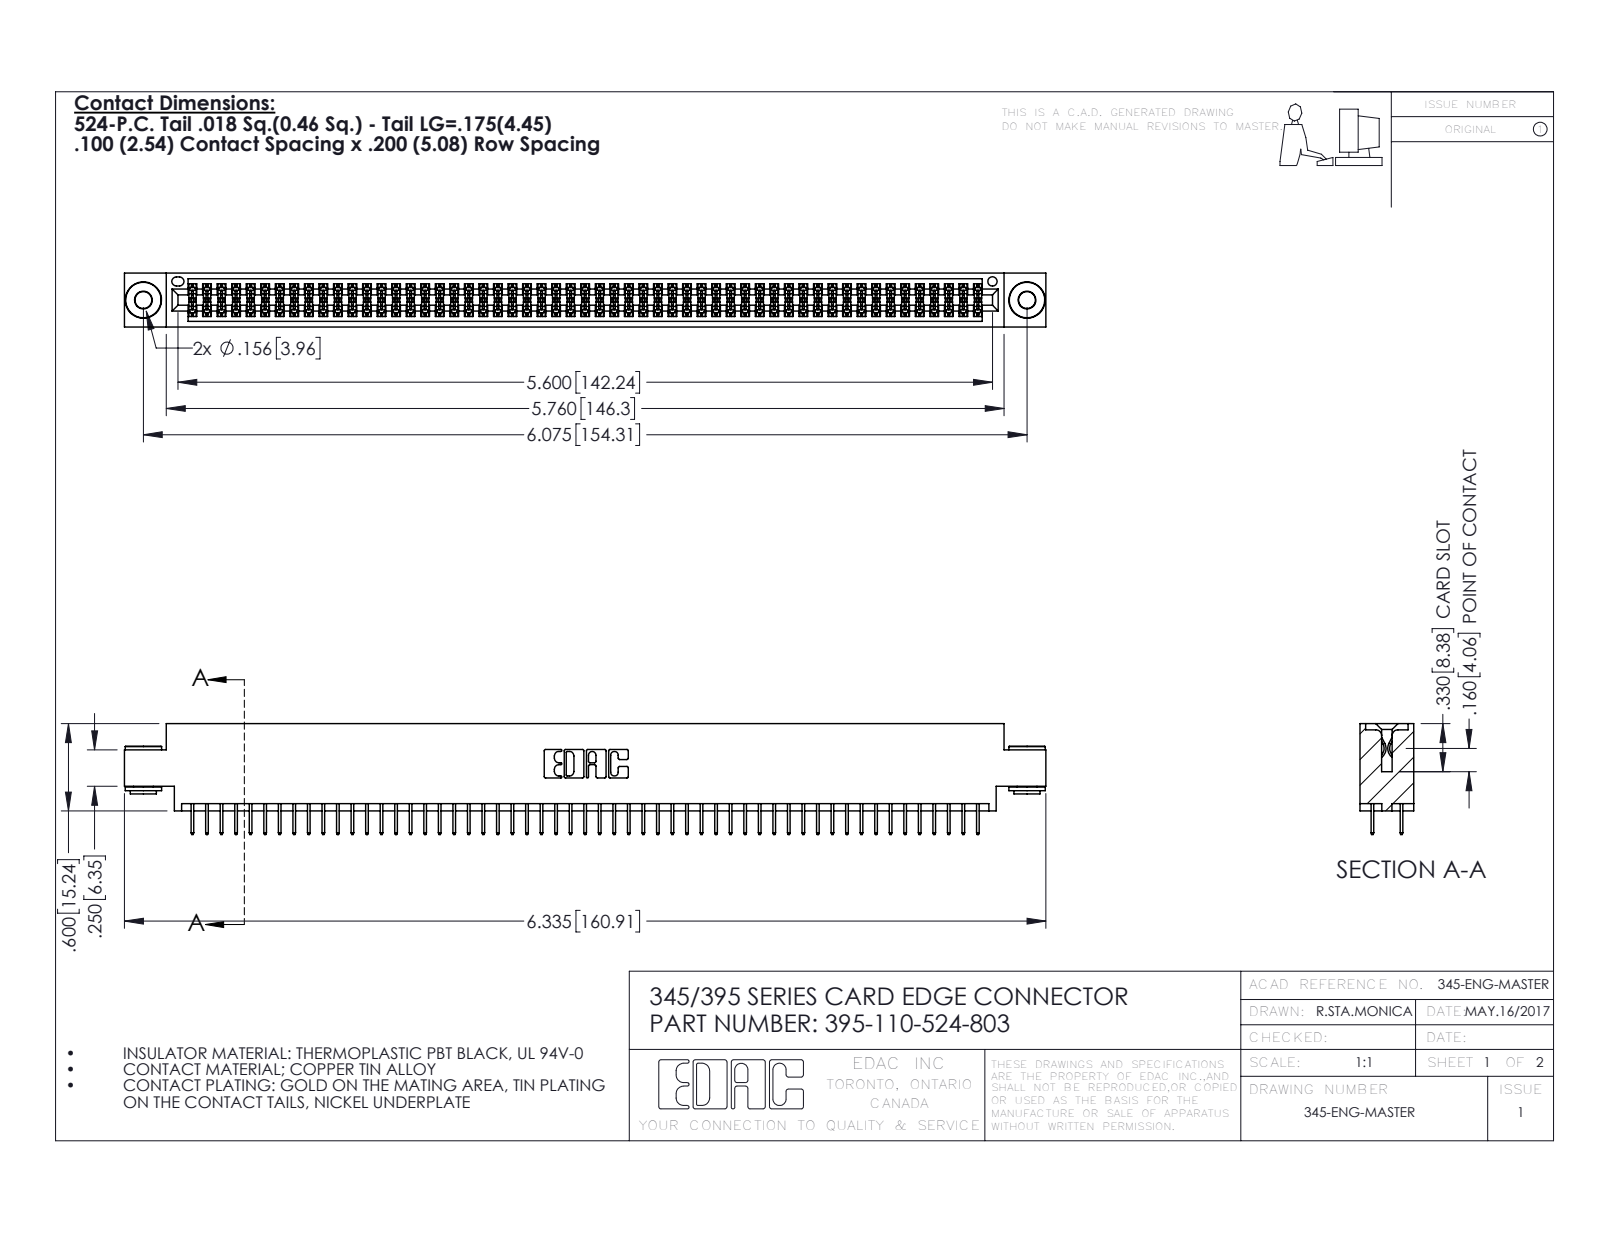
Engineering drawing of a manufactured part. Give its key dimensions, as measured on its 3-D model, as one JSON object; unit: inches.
{"part_name": "345-292-001_345-293-124; 345-250-002_345-250-002-102; 345 Part_0.170 Offset - 0.156 Dia-TH; 395-110-524-803", "step_written_by": "SolidWorks 2016 (CONFIG_CONTROL_DESIGN)", "units": "inches", "bodies": {"solids": 113, "faces": 6108, "planar": 4384, "cylindrical": 1716, "other": 8}, "overall_size": [6.335, 0.762, 0.37], "volume_in3": 0.945, "surface_area_in2": 35.74, "round_holes": [[0.116, 2], [0.156, 2], [0.064, 1]], "round_bosses_or_shafts": [[0.25, 2], [0.18, 2], [0.136, 2]], "partial_cylinders_radius": [[0.006, 165], [0.01, 22], [0.007, 6], [0.031, 6], [0.026, 3], [0.014, 2], [0.019, 2], [0.022, 2]], "face_to_face_distances": [0.072, 0.298, 0.37, 0.2, 0.098, 0.272, 0.025, 0.225, 0.175, 0.072], "hole_center_spacings": [0.27, 5.839, 6.075]}
